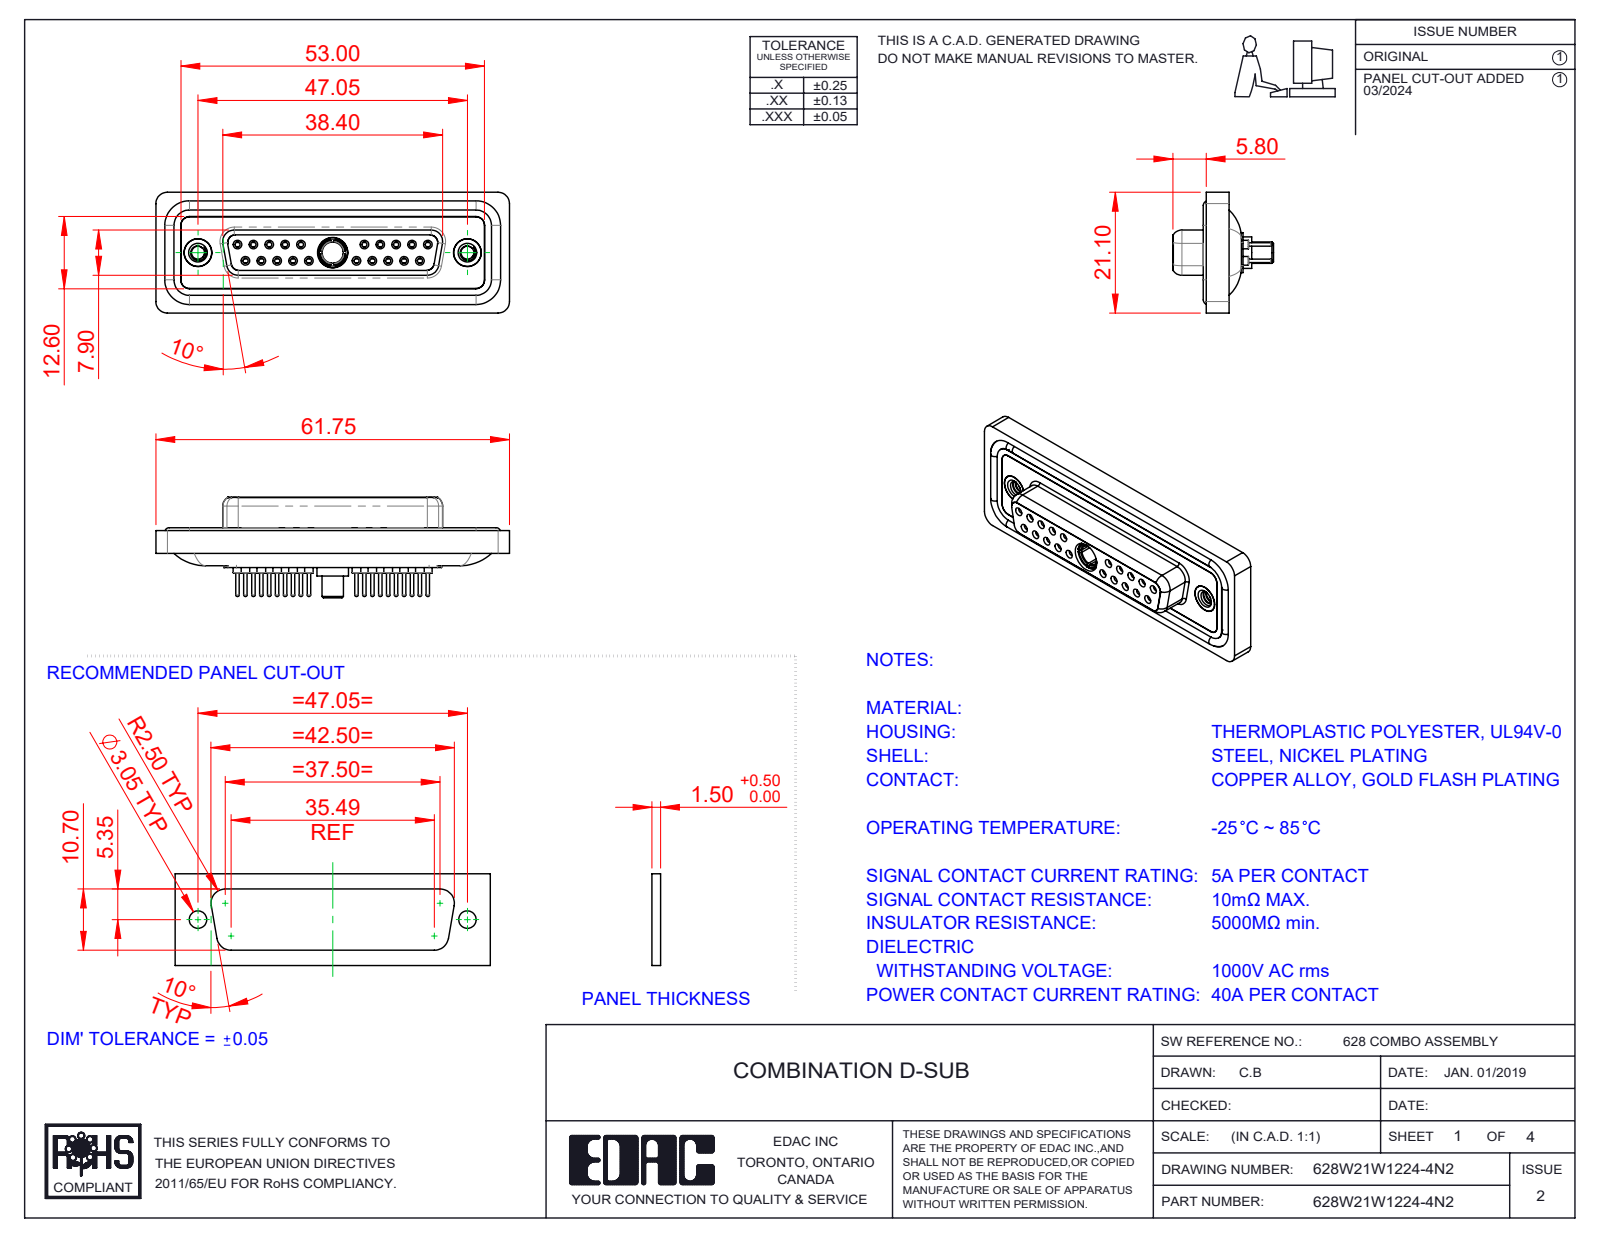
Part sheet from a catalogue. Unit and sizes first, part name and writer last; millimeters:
Units: millimetres
Overall size (bounding box): 61.75 × 21.1 × 17.55
Round holes (diameter × count): ⌀0.9 ×20, ⌀1.1 ×20, ⌀1.5 ×20, ⌀2 ×20, ⌀1.6 ×10, ⌀1.7 ×10, ⌀4.85 ×3, ⌀2.26 ×2, ⌀4 ×2, ⌀4.05 ×2, ⌀5 ×2, ⌀3.7 ×1
Round bosses / shafts (diameter × count): ⌀2.2 ×20, ⌀0.6 ×20, ⌀1.6 ×14, ⌀4.95 ×2, ⌀4.8 ×2, ⌀5.5 ×1, ⌀5.2 ×1, ⌀4.96 ×1
Partial cylindrical surfaces — rounded edges, fillets, slot ends (radius × count): R1.5 ×22, R2 ×18, R1.35 ×8, R1.6 ×8, R0.25 ×4, R0.5 ×4, R0.6 ×4, R0.65 ×4
Main face-to-face distances: 0.4, 1.8, 7.45, 6.6, 5.65, 0.5, 1.6, 7.05, 2.9, 1.1
Hole centre spacings: 3.16, 2.77, 5.54, 5.03, 8.31, 7.48, 16.62, 19.39
Volume: 8 393 mm³ · Surface area: 14 013 mm²
Bodies: 29 solids, 1560 faces (434 planar, 591 cylindrical, 535 other)
Part name (STEP PRODUCT): 628Combo Contact Row 1_24; 628Combo Contact Row 2_24; 628Combo Threaded Rivet_2; Power Socket_40A S (+5 more)
STEP written by: SolidWorks 2023 (CONFIG_CONTROL_DESIGN)
